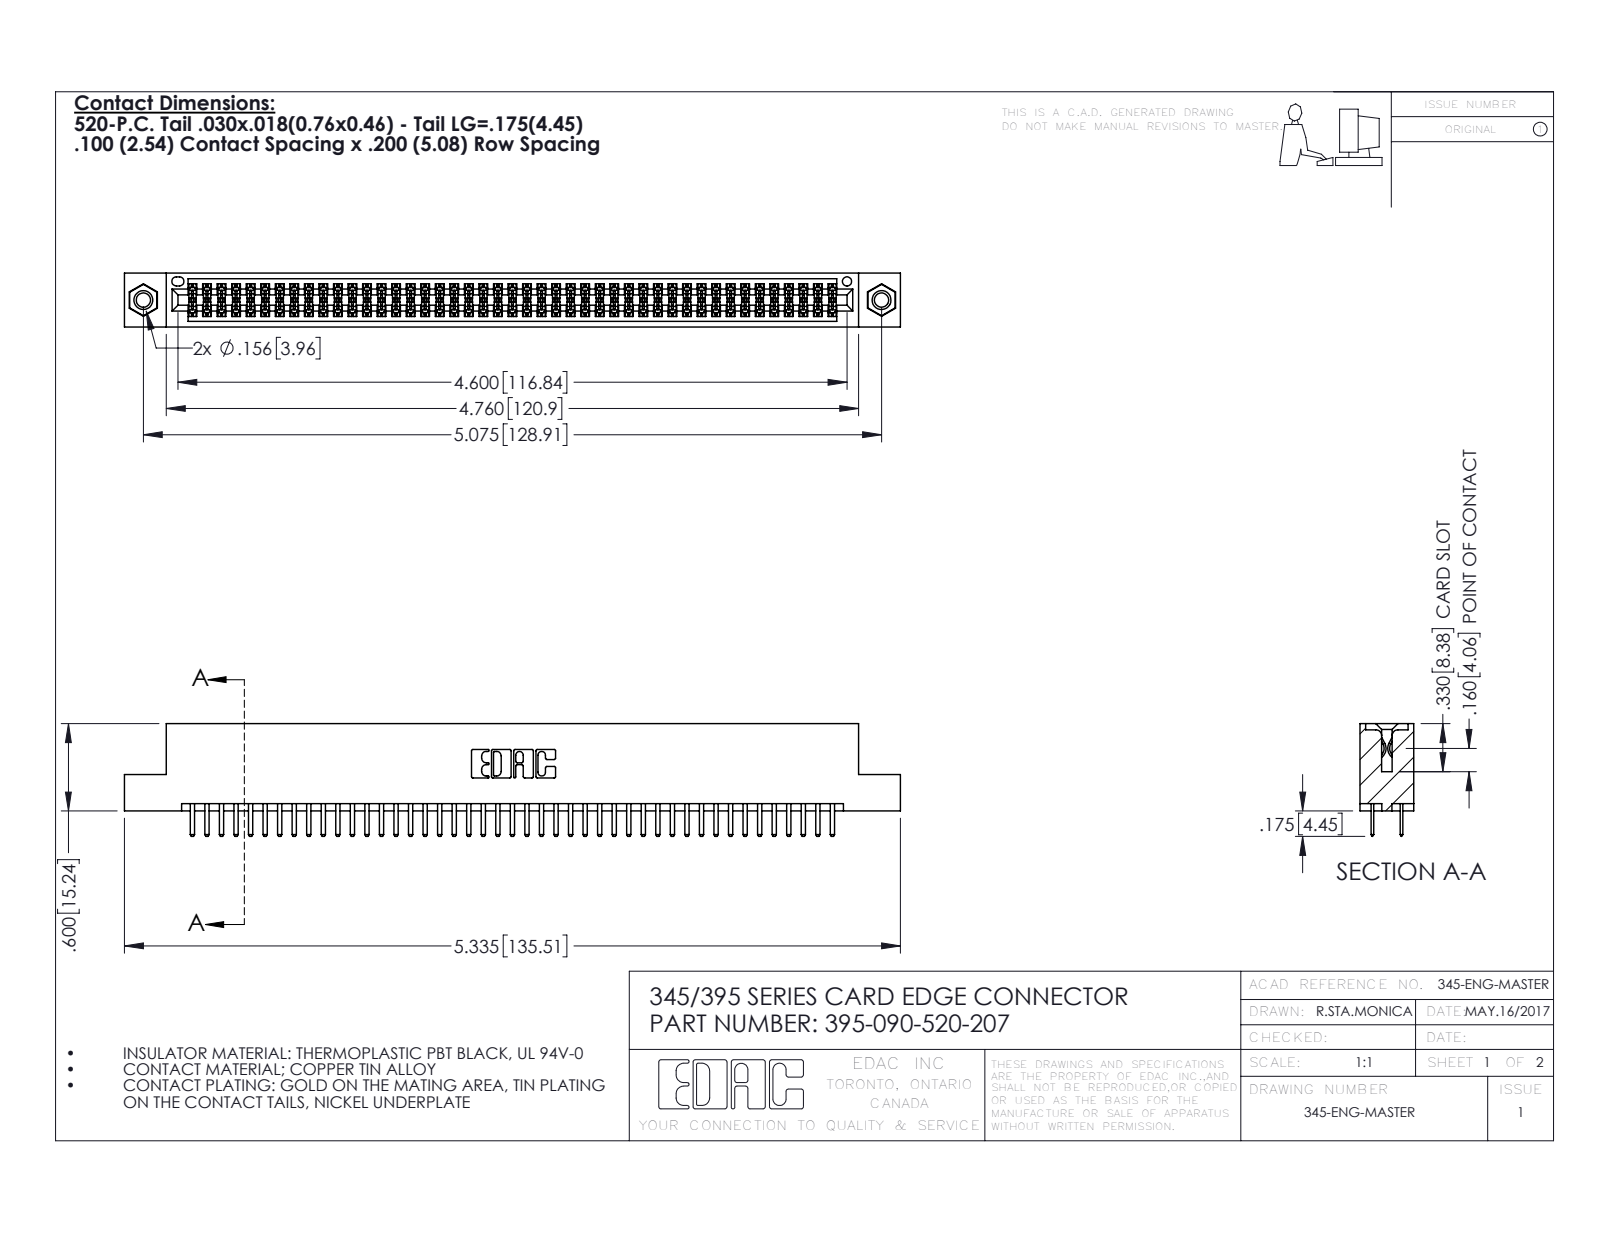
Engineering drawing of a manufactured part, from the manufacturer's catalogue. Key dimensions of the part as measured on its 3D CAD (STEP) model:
Part name (STEP PRODUCT): 345-250-001_345-250-005-103; 345 Part_Flush Mounting Lugs - 0.156 Dia-TI; 345-292-001_345-293-120; 395-090-520-207
STEP written by: SolidWorks 2016 (CONFIG_CONTROL_DESIGN)
Units: inches
Bodies: 93 solids, 5046 faces (3262 planar, 1768 cylindrical, 16 other)
Overall size (bounding box): 5.335 × 0.775 × 0.37
Volume: 0.802 in³ · Surface area: 30.1 in²
Round holes (diameter × count): ⌀0.098 ×2, ⌀0.125 ×2, ⌀0.156 ×2, ⌀0.064 ×1
Round bosses / shafts (diameter × count): ⌀0.155 ×2
Partial cylindrical surfaces — rounded edges, fillets, slot ends (radius × count): R0.006 ×135, R0.01 ×94, R0.01 ×22, R0.007 ×6, R0.031 ×6, R0.026 ×3, R0.014 ×2, R0.019 ×2
Main face-to-face distances: 0.072, 0.298, 0.2, 0.37, 0.098, 0.272, 0.025, 0.225, 0.022, 0.072
Hole centre spacings: 0.27, 4.839, 5.075
